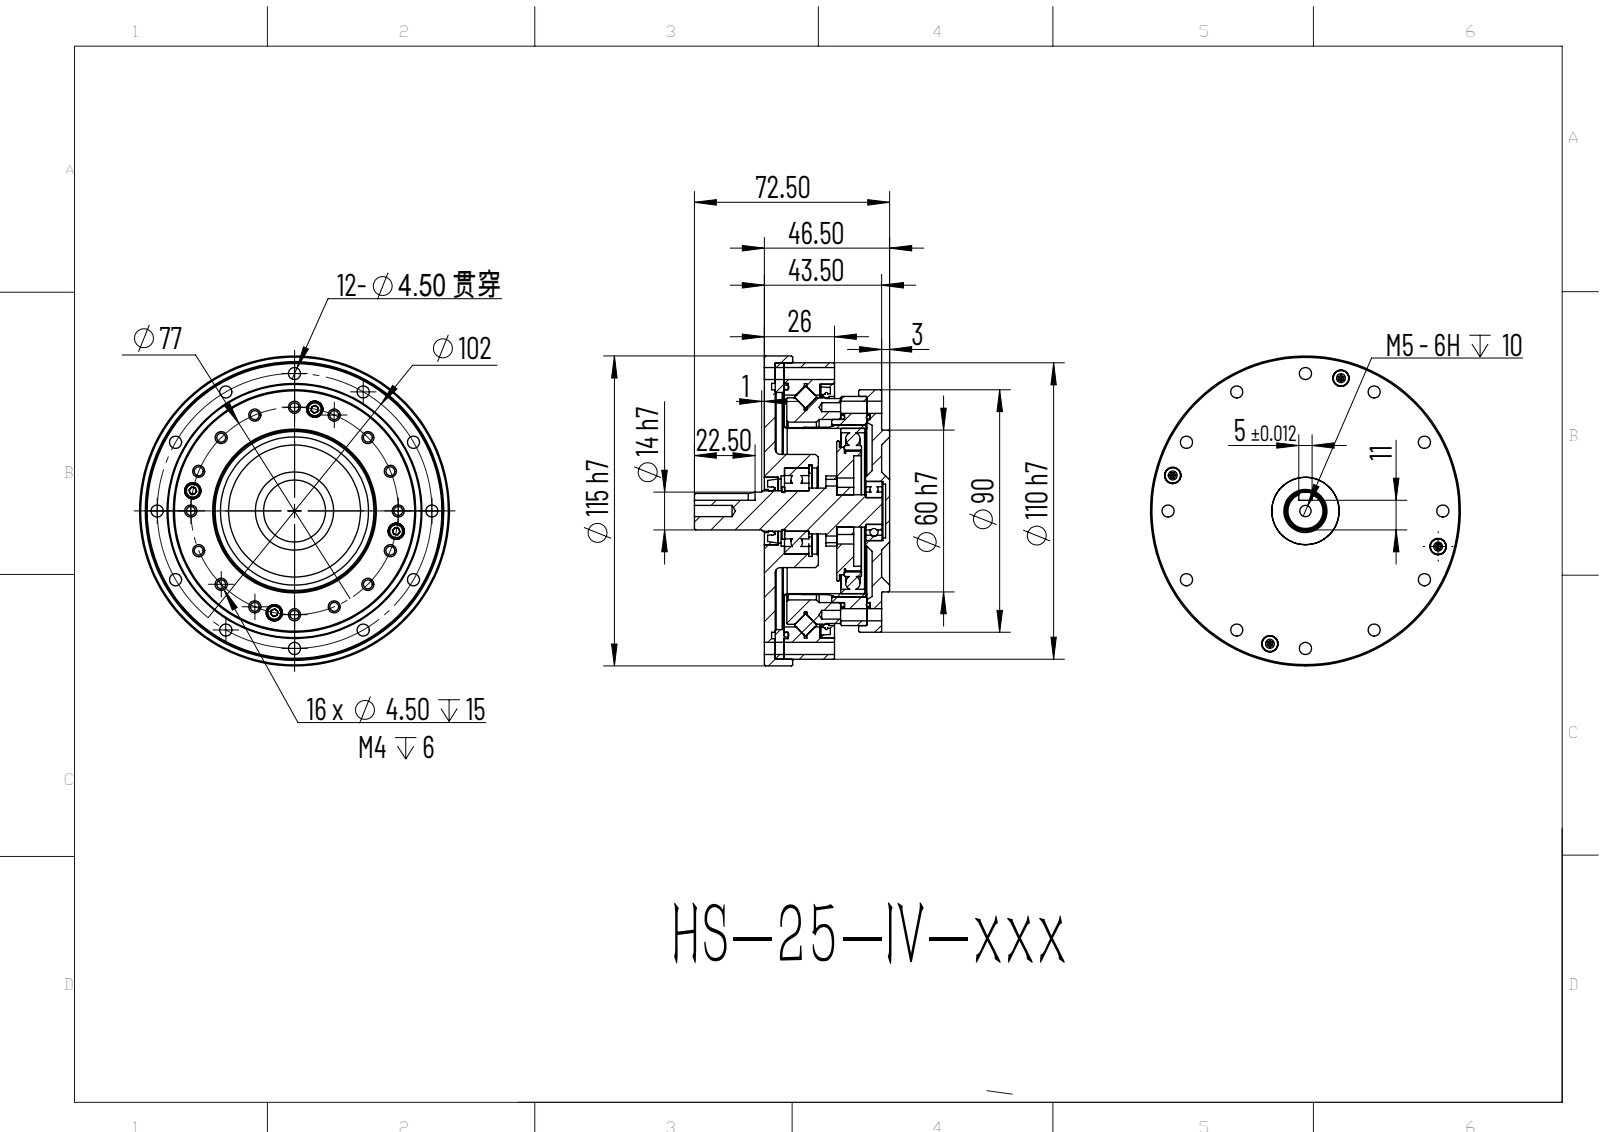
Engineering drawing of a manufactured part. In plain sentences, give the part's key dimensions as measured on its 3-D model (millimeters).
The part is named "HS-25-IV; hexagon socket head cap screws gb_GB_FASTENER_SCREWS_HSHCS M3X8-C; hexagon socket button head screws gb_GB_SOCKET_TYPE7 M3X8-N; circlips for shaft--type a large gb_GB_CONNECTING_PIECE_RING_RRA 15 (+8 more)". Its 3-D file was written by "ONSHAPE BY PTC INC, 1.201 (AP242_MANAGED_MODEL_BASED_3D_ENGINEERING_MIM_LF)". It is 104 solids with 1287 faces: 598 planar, 361 cylindrical and 328 other. Overall it measures 115 by 115 by 72.5 millimeters. Its volume is 262 011 cubic millimeters and its surface area 181 203 square millimeters. Round holes: 28 of diameter 4.5, 16 of diameter 3.3, 14 of diameter 2.5, 8 of diameter 3.4, 8 of diameter 3.5, 8 of diameter 6, 2 of diameter 1.7, 1 of diameter 2.05, 1 of diameter 2.9, 1 of diameter 4.2, 1 of diameter 5, 1 of diameter 10. Round bosses or shafts: 36 of diameter 6, 8 of diameter 3, 4 of diameter 5.5, 1 of diameter 115, 1 of diameter 110, 1 of diameter 90, 1 of diameter 84, 1 of diameter 83.5. Partial cylindrical surfaces (rounded edges, fillets, slot ends): 36 of radius 3.02, 3 of radius 2.5, 2 of radius 0.2, 2 of radius 0.5, 2 of radius 1.5, 1 of radius 8.4, 1 of radius 10.5, 1 of radius 14.8. The main face-to-face distances are 4, 7.3, 3.3, 5.5, 17.5, 26, 43.5, 39.5, 36.2, 22. The hole center spacings are 38.5, 42.78, 54.45, 15.02, 75.52, 29.47, 71.14, 77.
